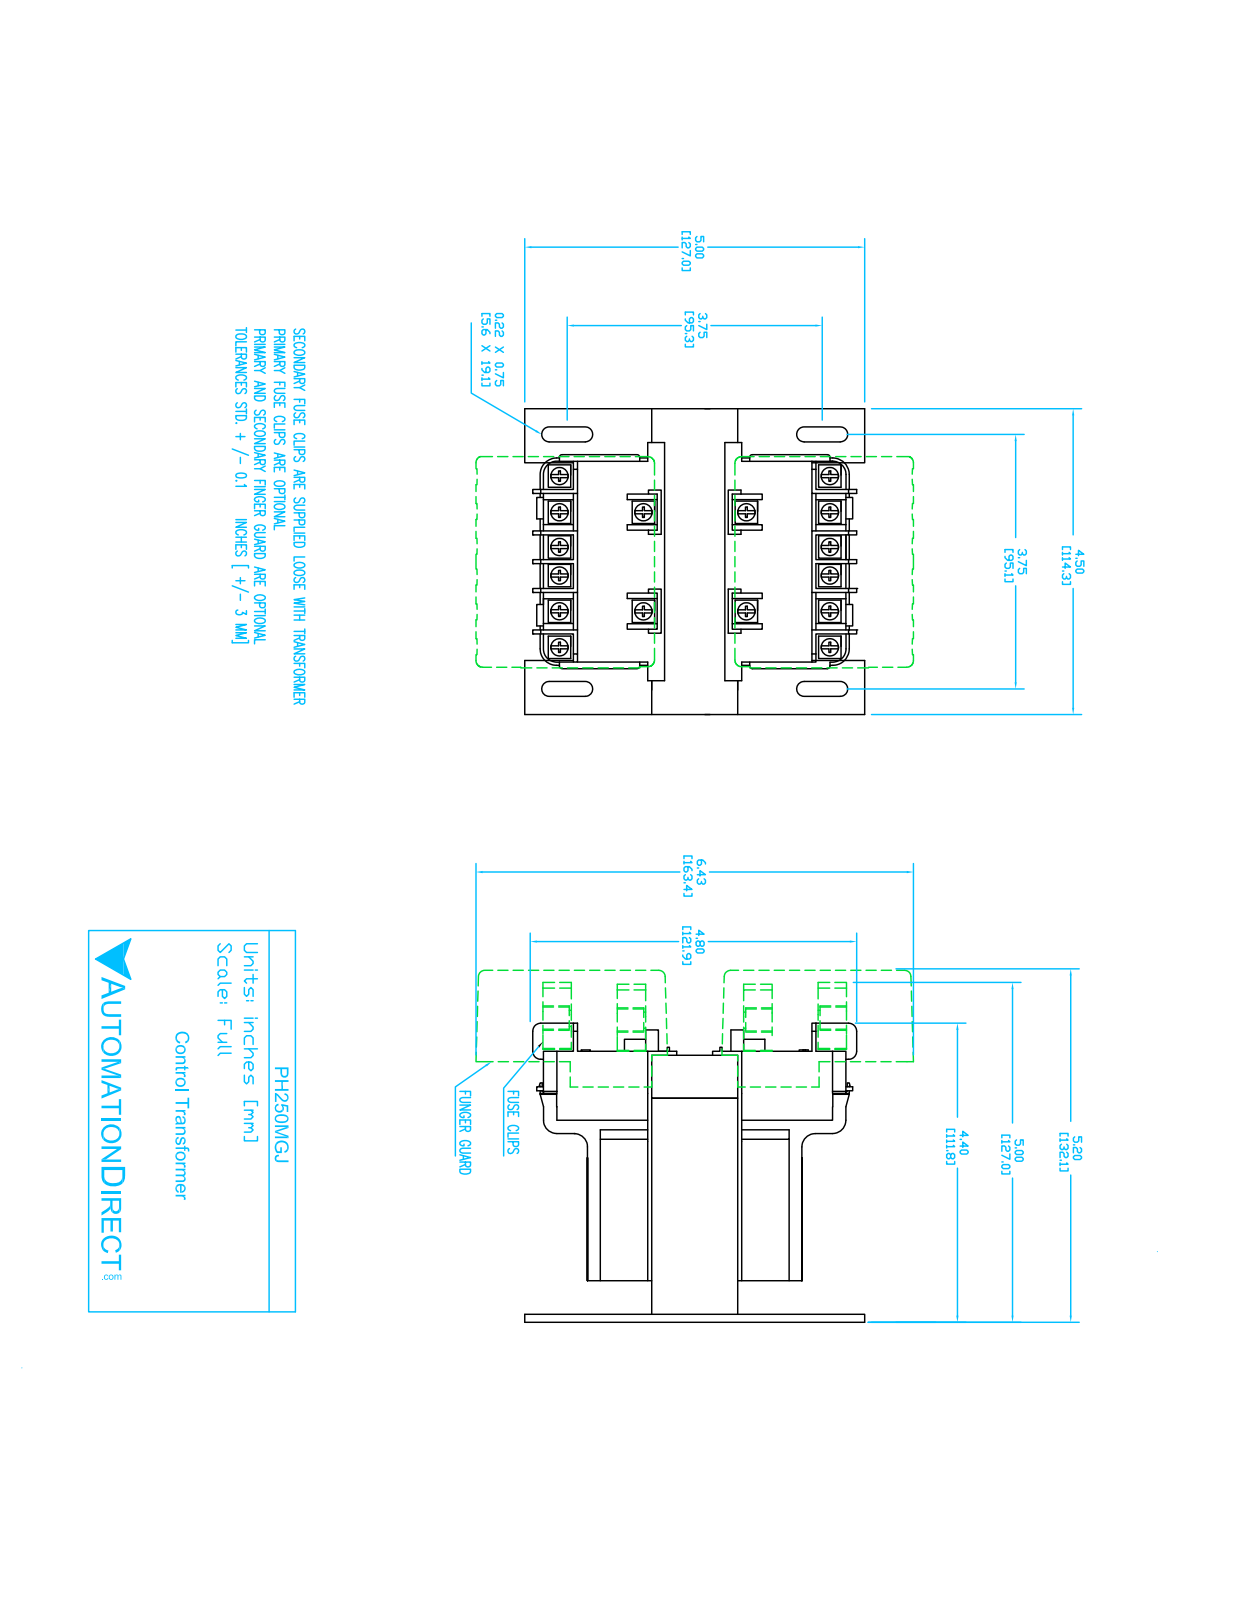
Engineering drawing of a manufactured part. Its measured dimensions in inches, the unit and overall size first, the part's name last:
Units: inches
Overall size (bounding box): 5 × 4.5 × 4.331
Round holes (diameter × count): ⌀0.157 ×8
Partial cylindrical surfaces — rounded edges, fillets, slot ends (radius × count): R0.039 ×86, R0.197 ×18, R0.11 ×8, R0.1 ×4, R0.243 ×4
Main face-to-face distances: 1.26, 3.858, 1.033, 3.179, 4.213, 2.992, 0.187, 1.22, 0.63, 3.228
Hole centre spacings: 3.75, 3.991, 0.383, 1.367, 3.769, 0.984, 3.877, 4.138
Volume: 58.29 in³ · Surface area: 207.9 in²
Bodies: 8 solids, 654 faces (382 planar, 194 cylindrical, 78 other)
Part name (STEP PRODUCT): PH250MGJ
STEP written by: SolidWorks 2017 (AUTOMOTIVE_DESIGN)
